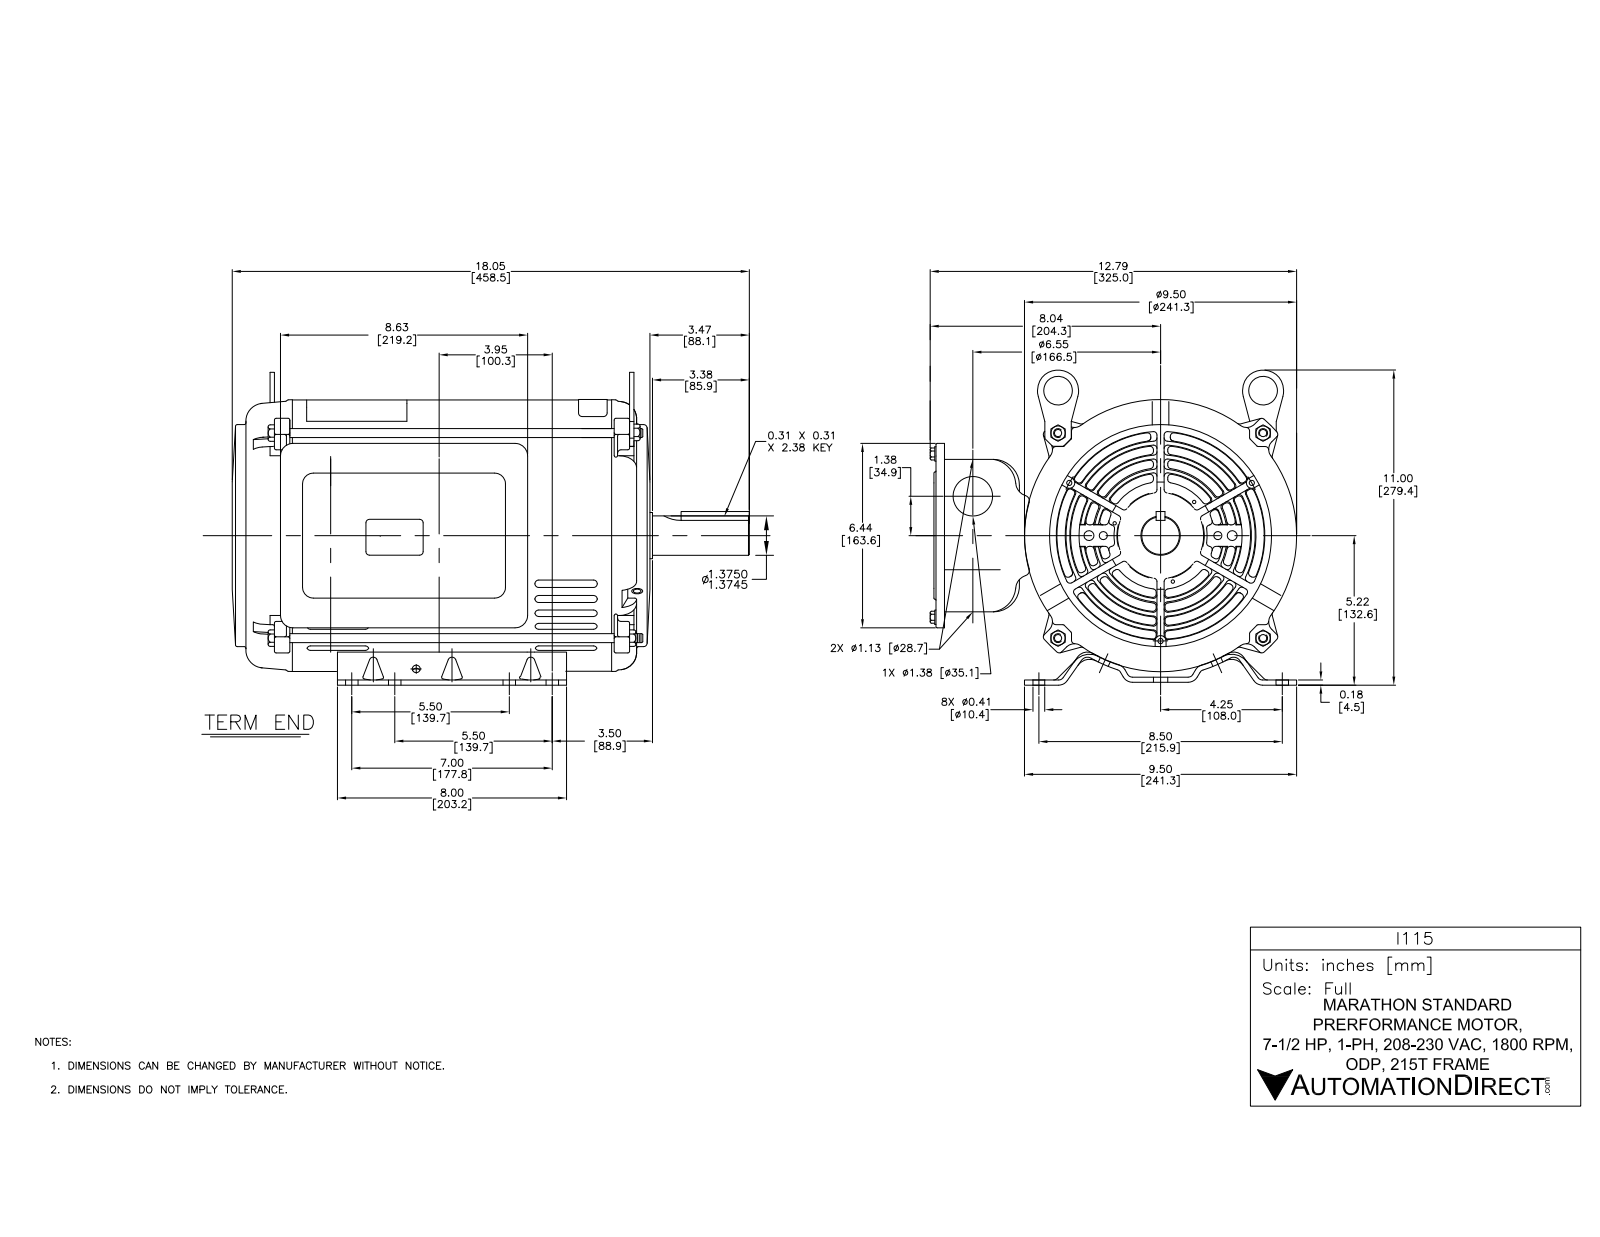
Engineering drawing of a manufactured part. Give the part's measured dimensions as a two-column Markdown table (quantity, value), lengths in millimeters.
| quantity | value |
| --- | --- |
| part name | I115 037642-1115_Rev002 B1 |
| STEP written by | SolidWorks 2017 (AUTOMOTIVE_DESIGN) |
| units | millimeters |
| bodies | 35 solids, 3896 faces (1399 planar, 849 cylindrical, 1648 other) |
| overall size | 460.7 × 330.1 × 279.6 |
| volume | 2 653 000 mm³ |
| surface area | 1 348 000 mm² |
| round holes (diameter × count) | 9.5 × 10, 3.9 × 6, 5.6 × 6, 11 × 6, 7.1 × 5, 5.4 × 4, 6.5 × 4, 25.4 × 4, 3.2 × 3, 4.4 × 3, 7.6 × 3, 2.5 × 2 |
| round bosses / shafts (diameter × count) | 6.4 × 7, 13.2 × 5, 8.4 × 4, 7.9 × 4, 17.3 × 2, 12.7 × 2, 9.7 × 2, 8.9 × 2 |
| partial cylindrical surfaces (radius × count) | 3.4 × 72, 0.8 × 48, 6.4 × 32, 1.5 × 28, 3 × 26, 4.8 × 14, 2 × 12, 0.5 × 10 |
| main face-to-face distances | 0.9, 1.9, 3.2, 2.8, 1.5, 6, 1.5, 5.1, 4.5, 4.5 |
| hole center spacings | 144.8, 63.5, 25.4, 181.8, 38.1, 88.9, 94.9, 99.3 |
